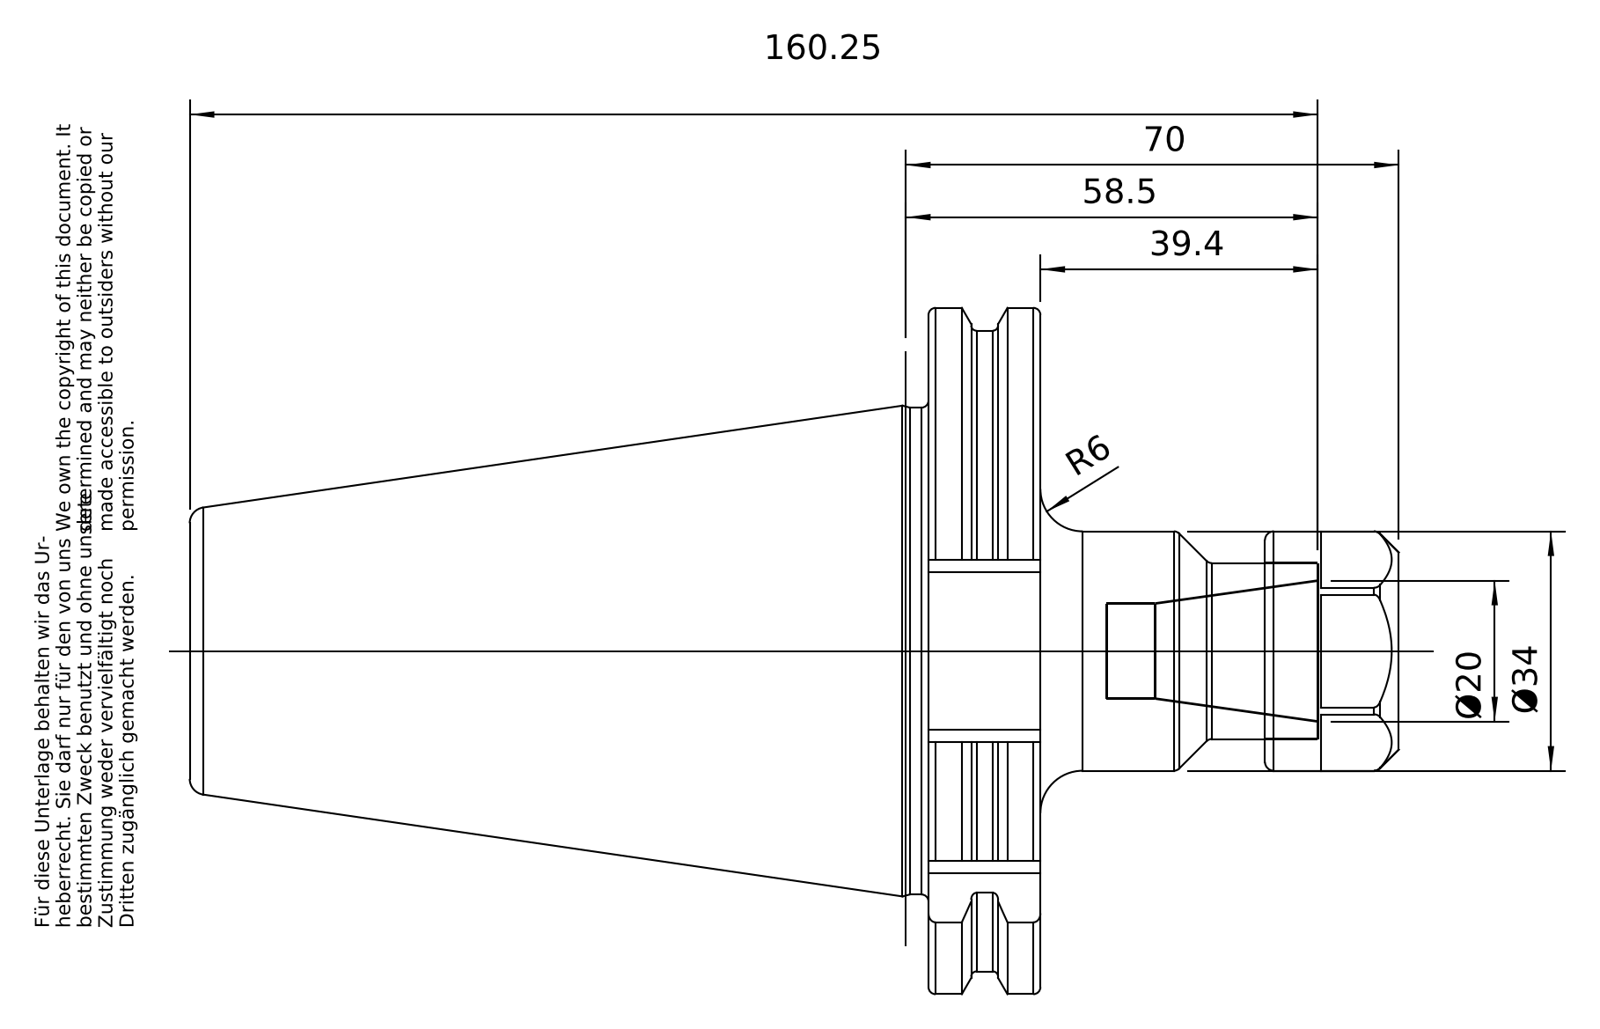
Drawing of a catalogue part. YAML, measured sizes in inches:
part_name: "50-320-20; 83-912-20; 50-320-20_ASM"
step_written_by: "PRO/ENGINEER BY PARAMETRIC TECHNOLOGY CORPORATION, 2010430 (CONFIG_CONTROL_DESIGN)"
units: inches
bodies: {solids: 2, faces: 129, planar: 29, cylindrical: 32, other: 68}
overall_size: [6.756, 3.837, 3.701]
volume: 23.07
surface_area: 78.63
round_holes:
  - {diameter: 0.531, count: 1}
  - {diameter: 0.817, count: 1}
  - {diameter: 0.985, count: 1}
  - {diameter: 1.012, count: 1}
round_bosses_or_shafts:
  - {diameter: 3.583, count: 1}
  - {diameter: 2.722, count: 1}
  - {diameter: 1.339, count: 1}
  - {diameter: 0.984, count: 1}
  - {diameter: 0.945, count: 1}
partial_cylinders:
  - {radius: 0.069, count: 5}
  - {radius: 1.919, count: 1}
face_to_face_distances: [0.624, 1.882, 1.258, 1.181, 2.63, 2.006, 0.748, 4.126, 4.75, 6.008]
